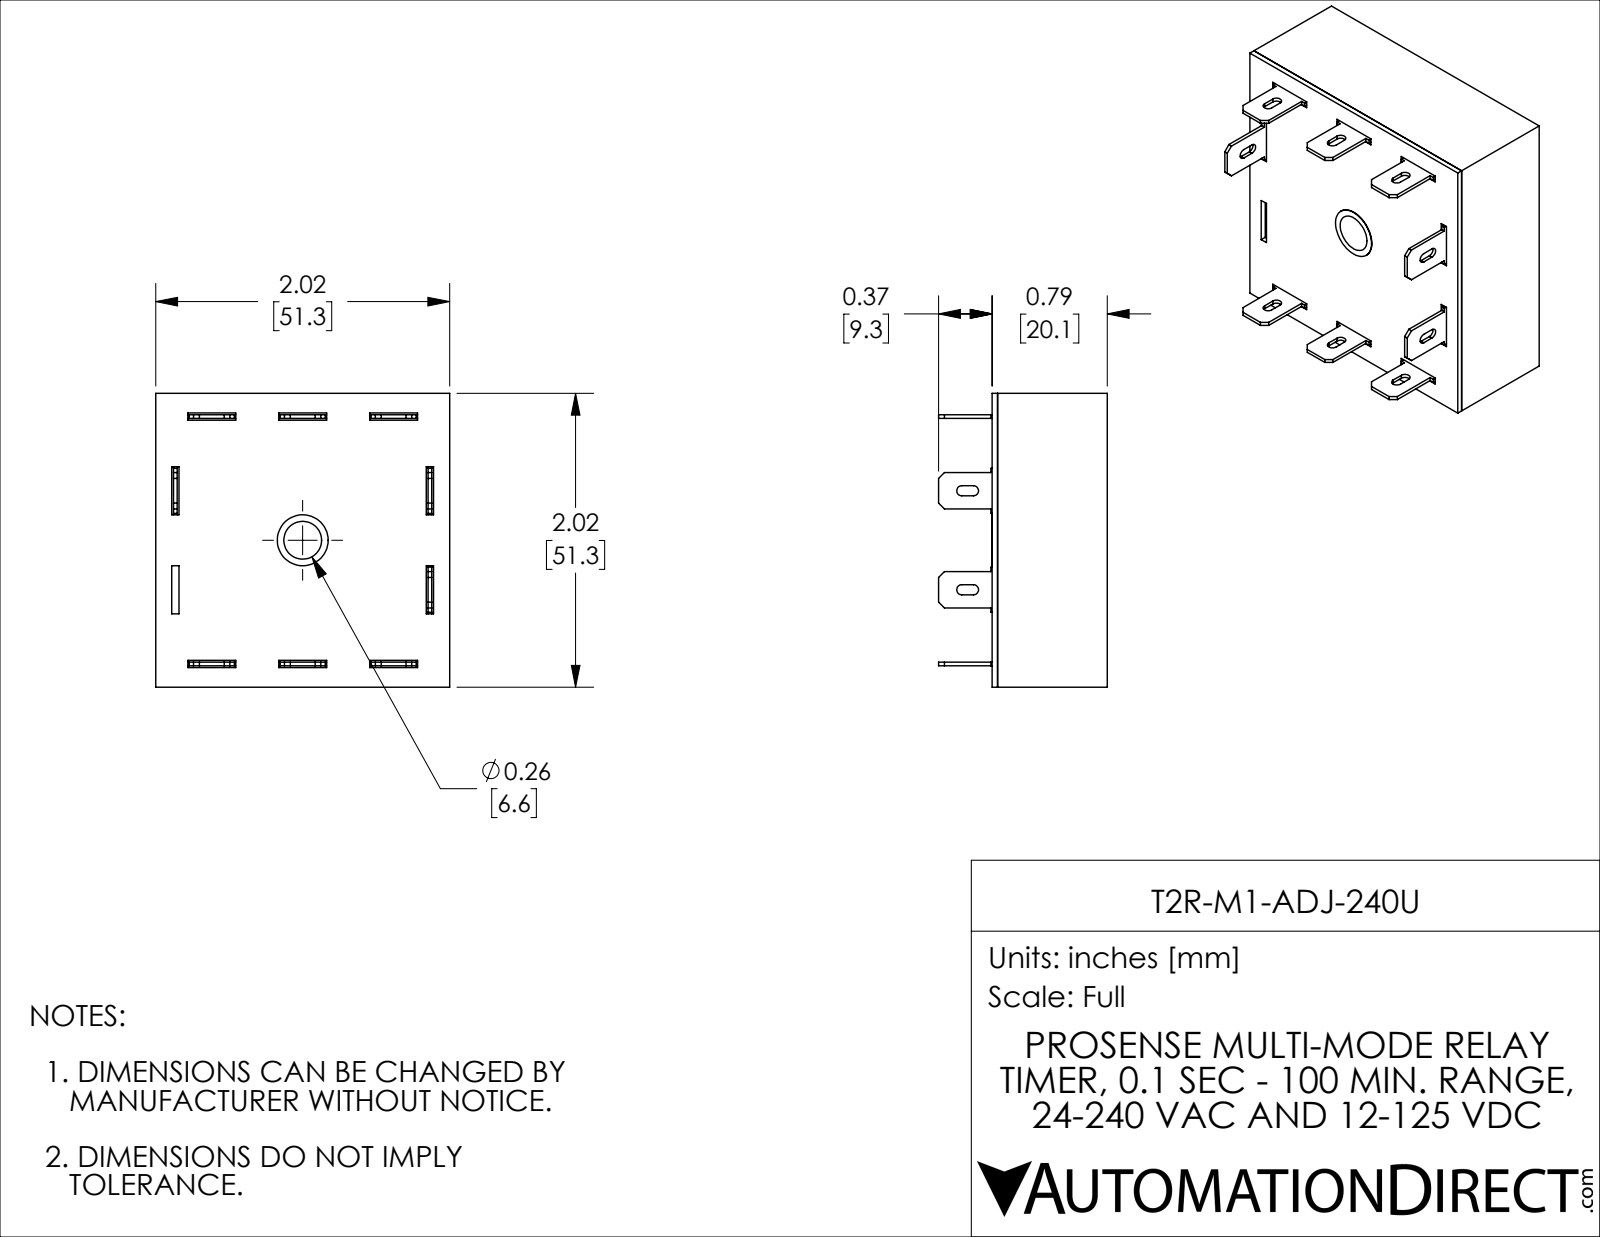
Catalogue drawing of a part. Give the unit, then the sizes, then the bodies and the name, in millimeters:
Units: millimetres
Overall size (bounding box): 51.31 × 51.31 × 29.46
Round holes (diameter × count): ⌀8.89 ×1
Partial cylindrical surfaces — rounded edges, fillets, slot ends (radius × count): R0.89 ×10
Main face-to-face distances: 1.14, 50.16, 19.15, 20.12, 0.97, 18.01, 18.98, 51.3, 3.74, 47.56
Volume: 11 178 mm³ · Surface area: 23 301 mm²
Bodies: 11 solids, 280 faces (256 planar, 22 cylindrical, 2 other)
Part name (STEP PRODUCT): T2R-M1-ADJ-240U
STEP written by: SolidWorks 2021 (CONFIG_CONTROL_DESIGN)
